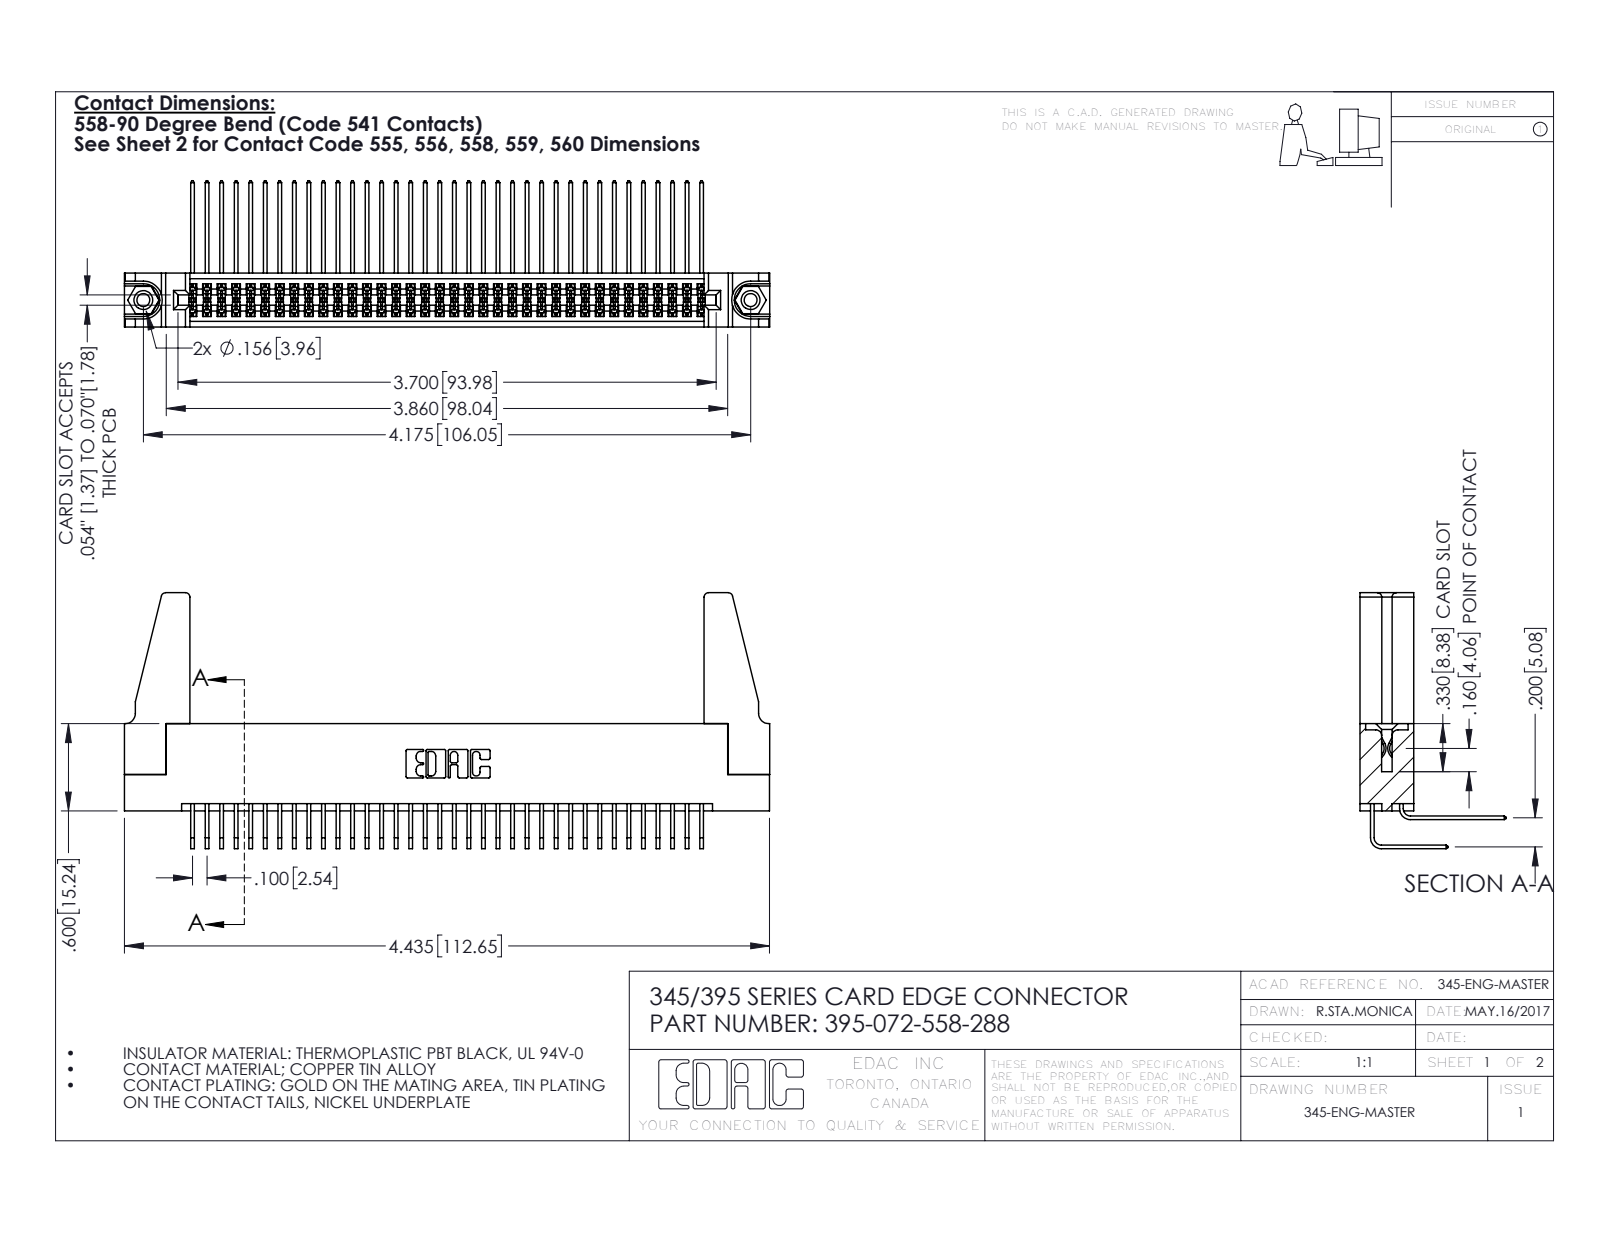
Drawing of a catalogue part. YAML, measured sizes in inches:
part_name: "345-292-001_558 Tail - 2; 345 Part_Flush Mounting Lugs - 0.156 Dia-TH; 345-220-078_345-220-088; 345-250-001_345-250-001-102 (+2 more)"
step_written_by: "SolidWorks 2016 (CONFIG_CONTROL_DESIGN)"
units: inches
bodies: {solids: 77, faces: 3994, planar: 2672, cylindrical: 1306, other: 16}
overall_size: [4.436, 1.759, 1.005]
volume: 0.888
surface_area: 33.59
round_holes:
  - {diameter: 0.089, count: 2}
  - {diameter: 0.125, count: 2}
  - {diameter: 0.156, count: 2}
  - {diameter: 0.064, count: 1}
round_bosses_or_shafts:
  - {diameter: 0.155, count: 2}
partial_cylinders:
  - {radius: 0.006, count: 108}
  - {radius: 0.01, count: 22}
  - {radius: 0.03, count: 8}
  - {radius: 0.007, count: 6}
  - {radius: 0.031, count: 6}
  - {radius: 0.026, count: 3}
  - {radius: 0.014, count: 2}
  - {radius: 0.019, count: 2}
face_to_face_distances: [0.072, 0.298, 0.2, 0.37, 0.098, 0.272, 0.025, 0.225, 0.285, 0.025]
hole_center_spacings: [0.27, 3.939, 4.175]
